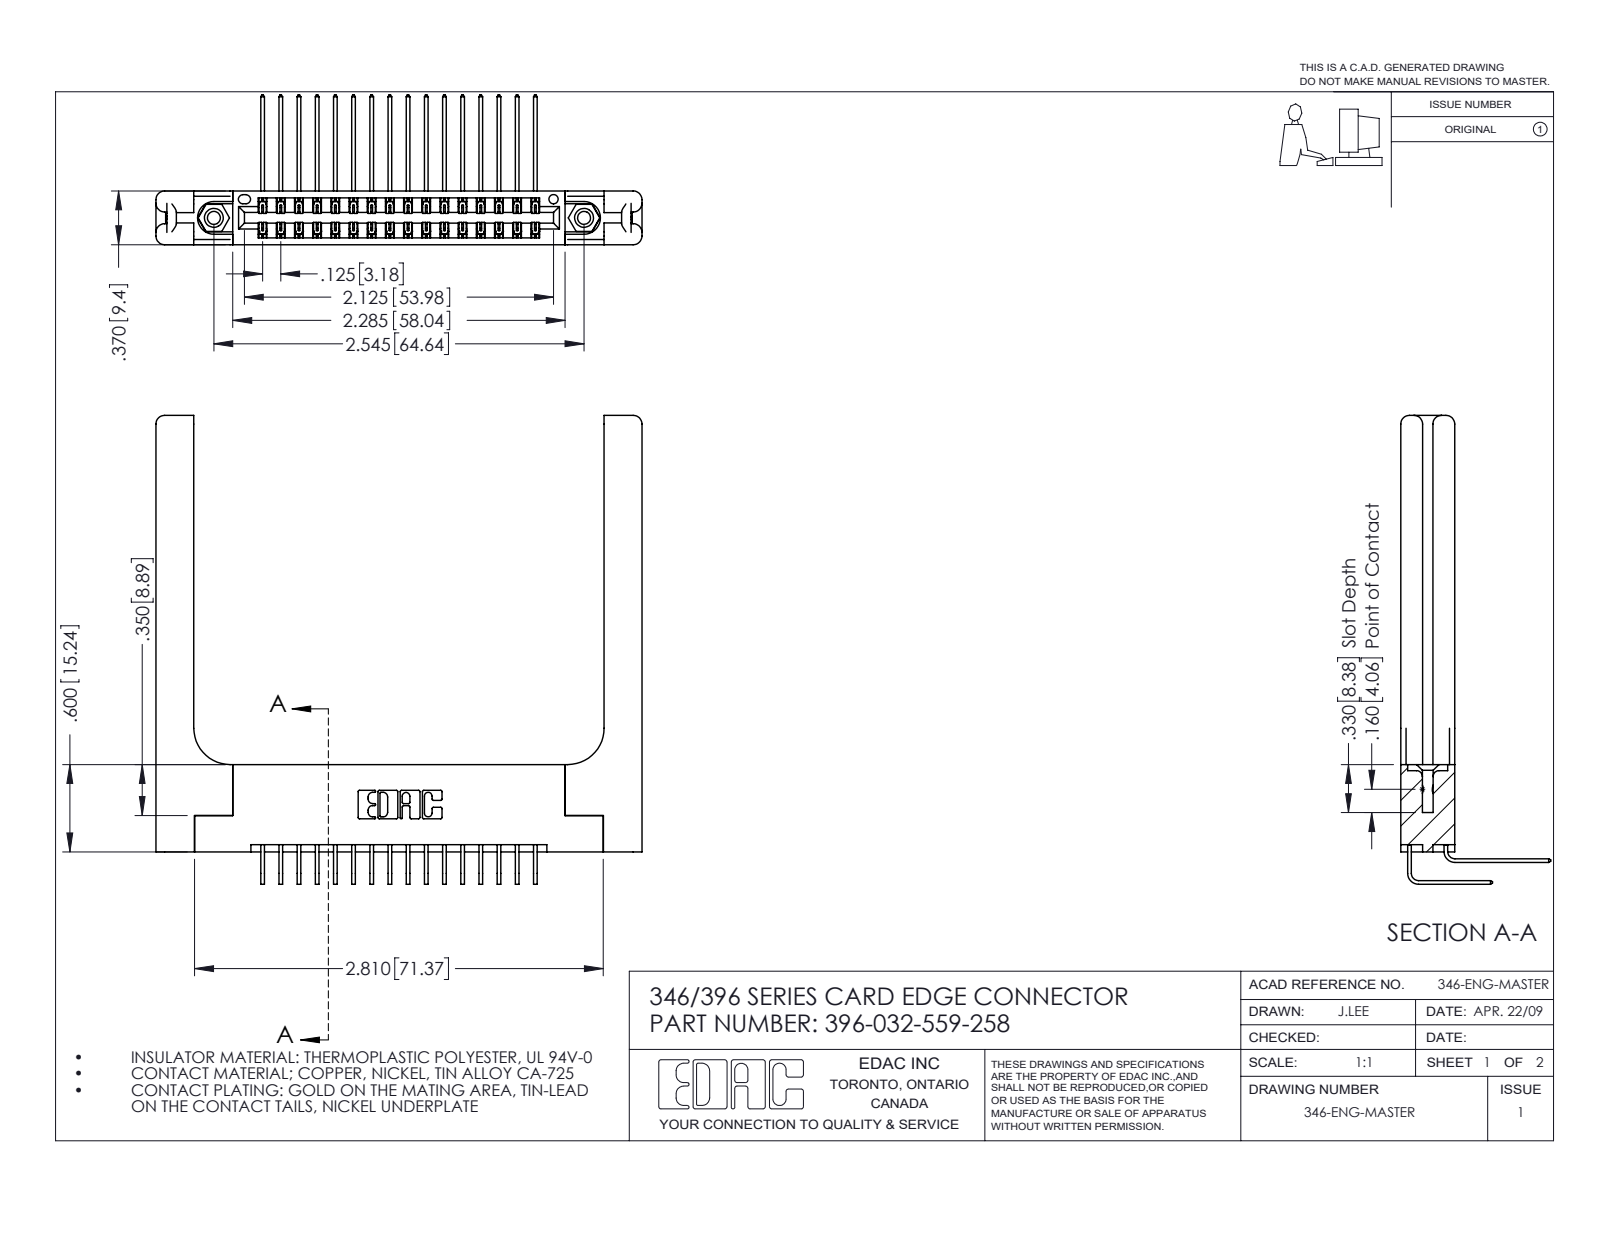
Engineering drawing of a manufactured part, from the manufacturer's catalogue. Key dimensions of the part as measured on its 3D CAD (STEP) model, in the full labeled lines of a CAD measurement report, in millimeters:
Part name (STEP PRODUCT): 345-292-001_559 Tail - 2; 345-250-001_345-250-001-102; 345-292-001_558 559 Tail - 1; 346 Part_Flush Mounting Lugs - 0.156 Dia-TH (+2 more)
STEP written by: SolidWorks 2016 (CONFIG_CONTROL_DESIGN)
Units: millimetres
Bodies: 37 solids, 2106 faces (1408 planar, 638 cylindrical, 60 other)
Overall size (bounding box): 84.9 × 81.9 × 26.2
Volume: 15 700 mm³ · Surface area: 16 800 mm²
Round holes (diameter × count): ⌀2.3 ×2, ⌀3.2 ×2, ⌀4 ×2, ⌀1.6 ×1
Round bosses / shafts (diameter × count): ⌀3.9 ×2
Partial cylindrical surfaces — rounded edges, fillets, slot ends (radius × count): R0.2 ×48, R0.3 ×22, R1.5 ×16, R0.2 ×6, R0.8 ×6, R0.7 ×3, R0.4 ×2, R0.6 ×2
Main face-to-face distances: 9.4, 1.8, 8.2, 1.2, 3.8, 3.8, 0.6, 6.4, 7.6, 2.6
Hole centre spacings: 6.2, 59.4, 64.6
